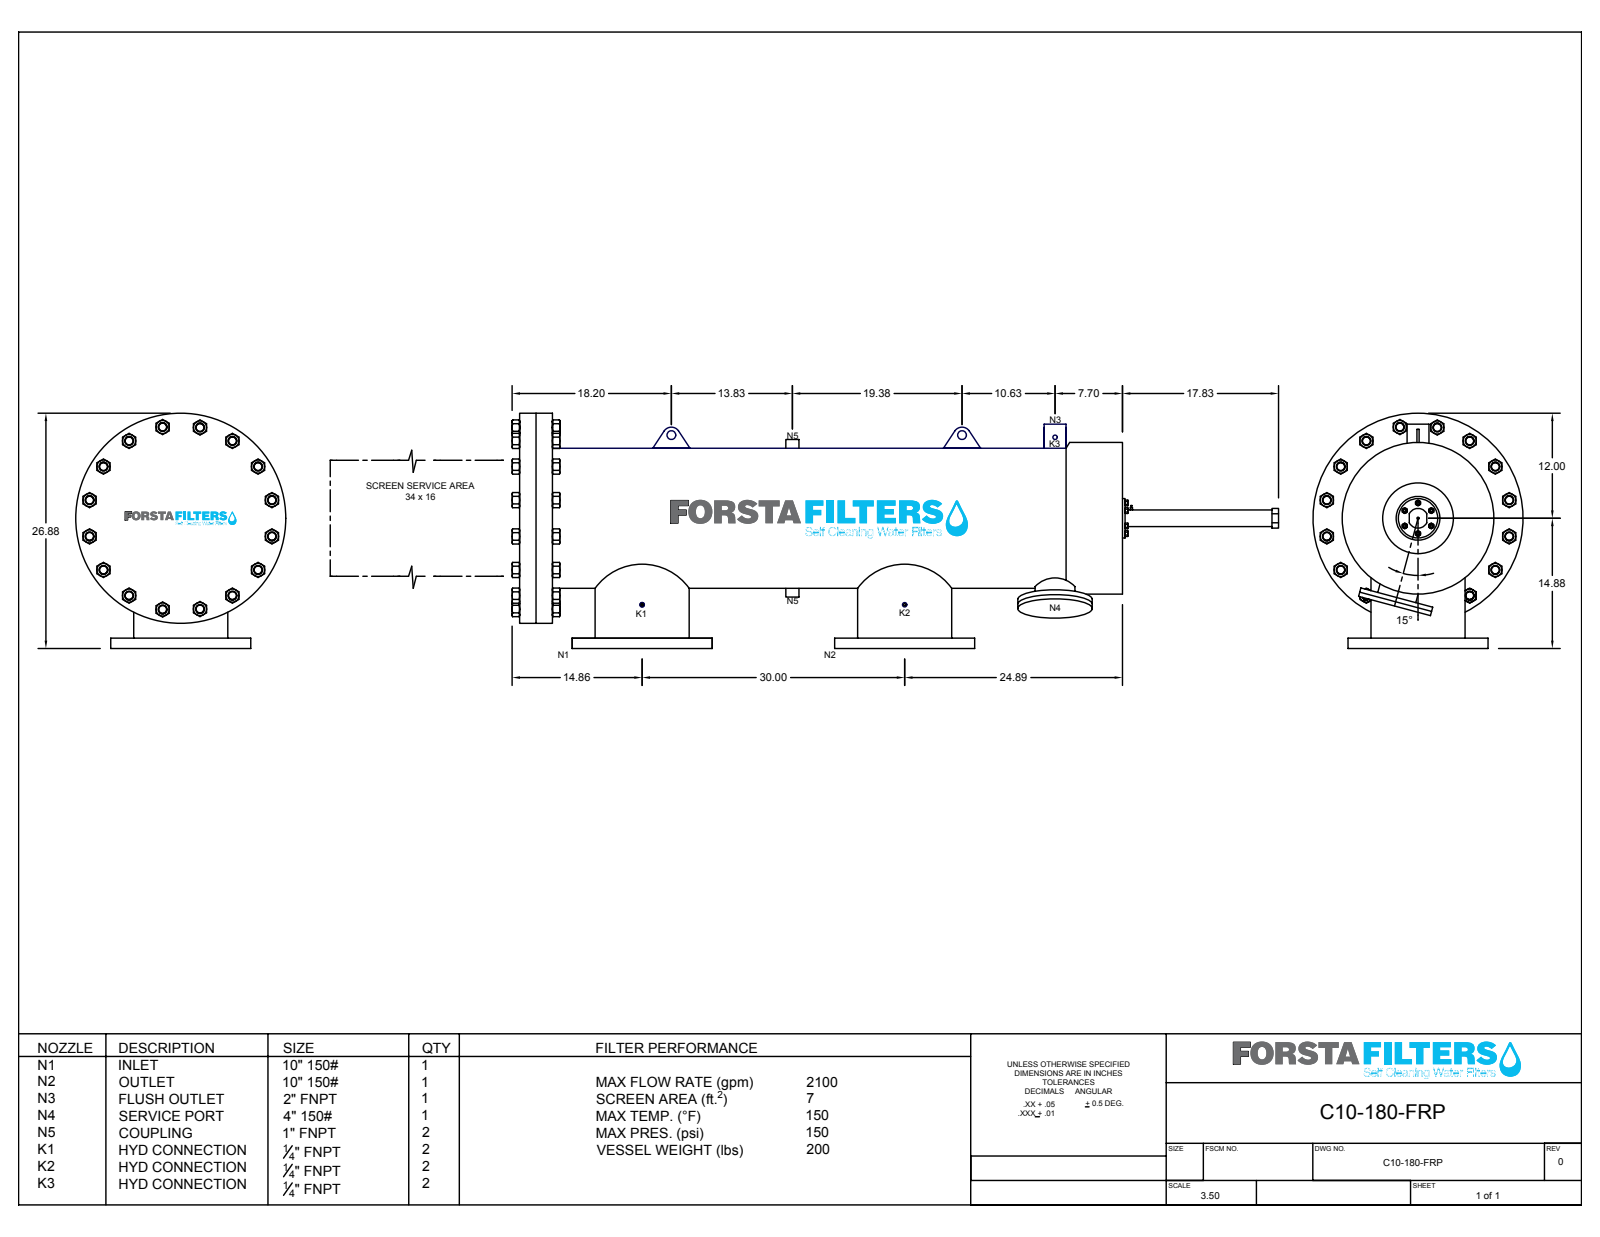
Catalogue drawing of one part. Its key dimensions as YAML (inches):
part_name: "C10-FRP-180"
step_written_by: "SolidWorks 2018 (CONFIG_CONTROL_DESIGN)"
units: inches
bodies: {solids: 23, faces: 699, planar: 363, cylindrical: 332, other: 4}
overall_size: [87.395, 26.88, 23.999]
volume: 2529
surface_area: 11435
round_holes:
  - {diameter: 1, count: 35}
  - {diameter: 0.75, count: 16}
  - {diameter: 0.25, count: 3}
  - {diameter: 4, count: 2}
  - {diameter: 10, count: 2}
  - {diameter: 0.246, count: 1}
  - {diameter: 1.507, count: 1}
  - {diameter: 2, count: 1}
  - {diameter: 15.603, count: 1}
  - {diameter: 16.934, count: 1}
round_bosses_or_shafts:
  - {diameter: 0.375, count: 6}
  - {diameter: 16, count: 2}
  - {diameter: 10.394, count: 2}
  - {diameter: 9, count: 2}
  - {diameter: 4.394, count: 2}
  - {diameter: 0.644, count: 2}
  - {diameter: 23.999, count: 1}
  - {diameter: 17.328, count: 1}
partial_cylinders:
  - {radius: 1, count: 2}
  - {radius: 1.125, count: 1}
face_to_face_distances: [1.875, 3.75, 1.875, 68.892, 67.017, 65.142, 68.695, 66.82, 64.945, 0.197]
hole_center_spacings: [2.87, 3.75, 4.146, 5.303, 6.929, 7.125, 8.132, 10.076]
